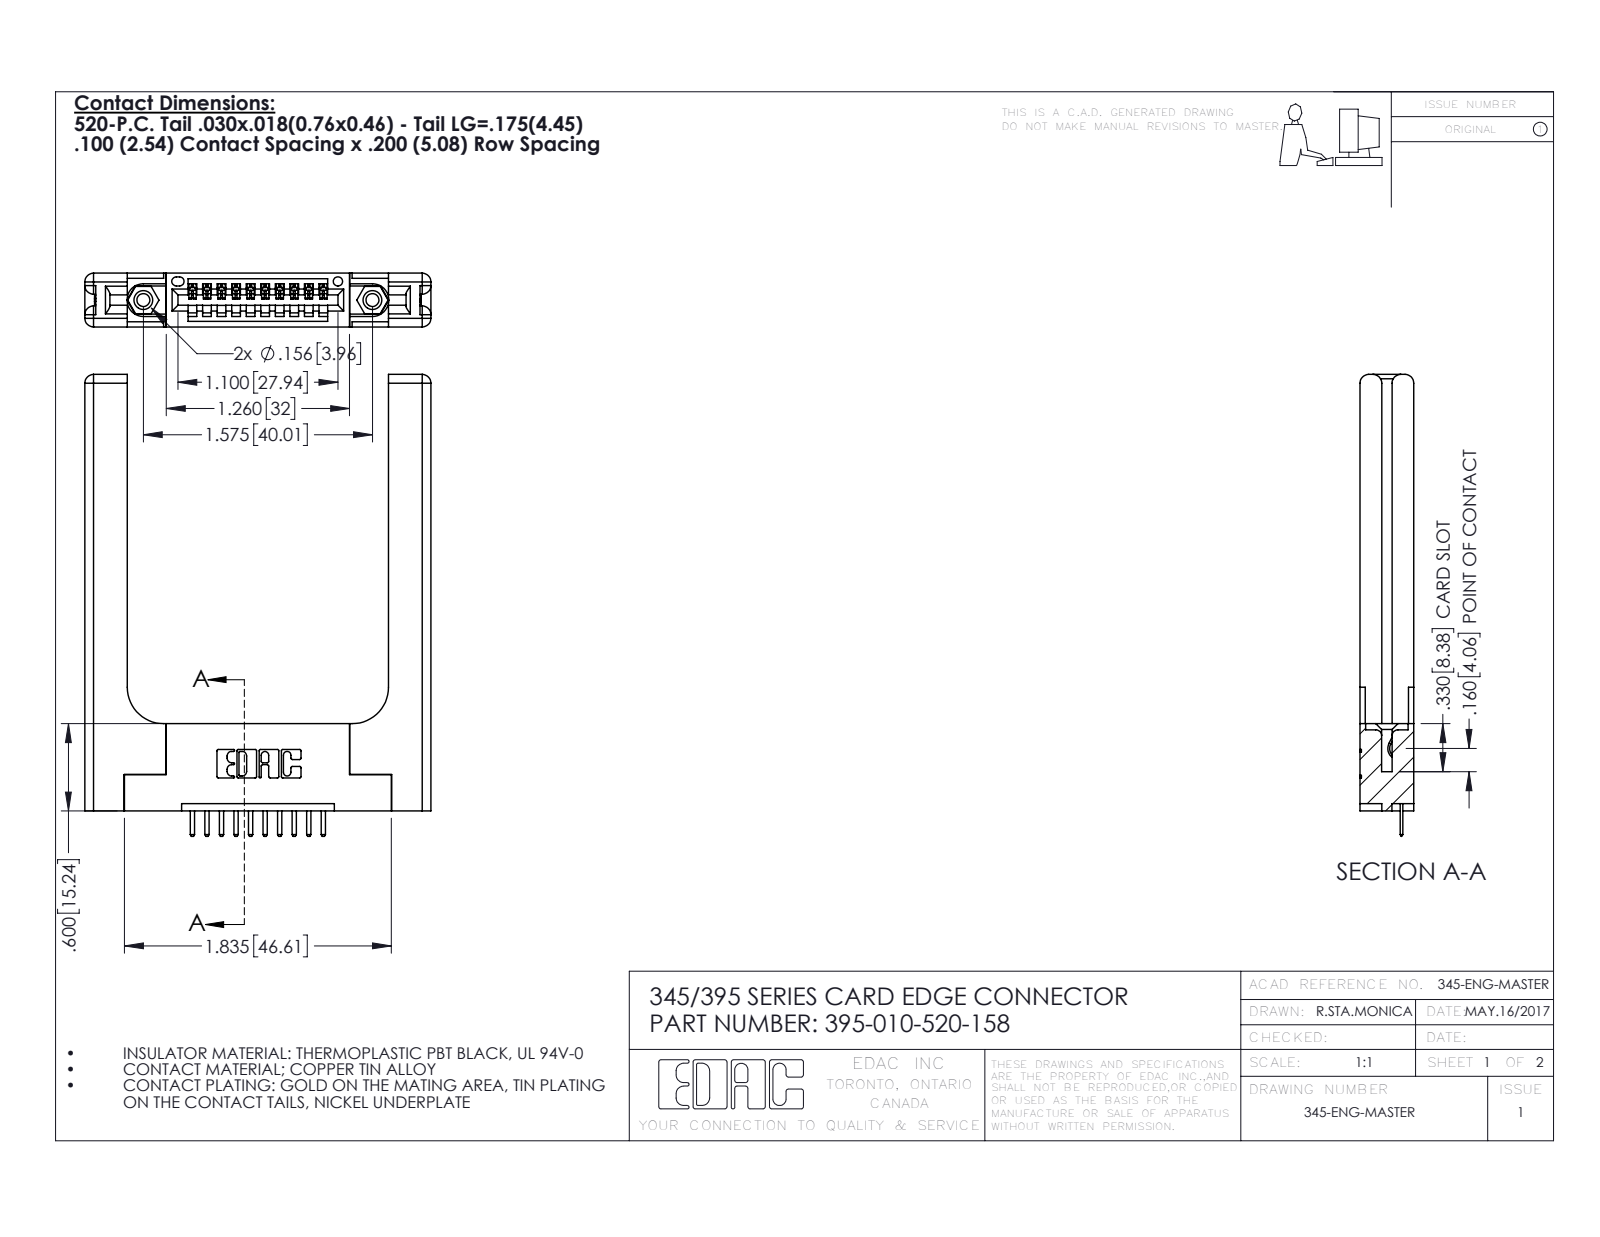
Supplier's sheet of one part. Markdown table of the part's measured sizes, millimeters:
| quantity | value |
| --- | --- |
| part name | 345-220-058_345-220-058; 345-250-001_345-250-001-102; 345-292-001_345-293-120; 345 Part_Flush Mounting Lugs - 0.156 Dia-TH (+1 more) |
| STEP written by | SolidWorks 2016 (CONFIG_CONTROL_DESIGN) |
| units | millimeters |
| bodies | 15 solids, 1002 faces (648 planar, 294 cylindrical, 60 other) |
| overall size | 80.6 × 60.4 × 9.4 |
| volume | 13 900 mm³ |
| surface area | 12 020 mm² |
| round holes (diameter × count) | 2.3 × 2, 3.2 × 2, 4 × 2, 1.6 × 1 |
| round bosses / shafts (diameter × count) | 3.9 × 2 |
| partial cylindrical surfaces (radius × count) | 0.3 × 22, 0.3 × 22, 0.2 × 20, 1.5 × 16, 0.2 × 6, 0.8 × 6, 0.7 × 3, 0.8 × 2 |
| main face-to-face distances | 9.4, 3.8, 5.6, 1.8, 2, 3.8, 7.6, 5.1, 45.6, 1.8 |
| hole center spacings | 6.9, 34.1, 40 |
